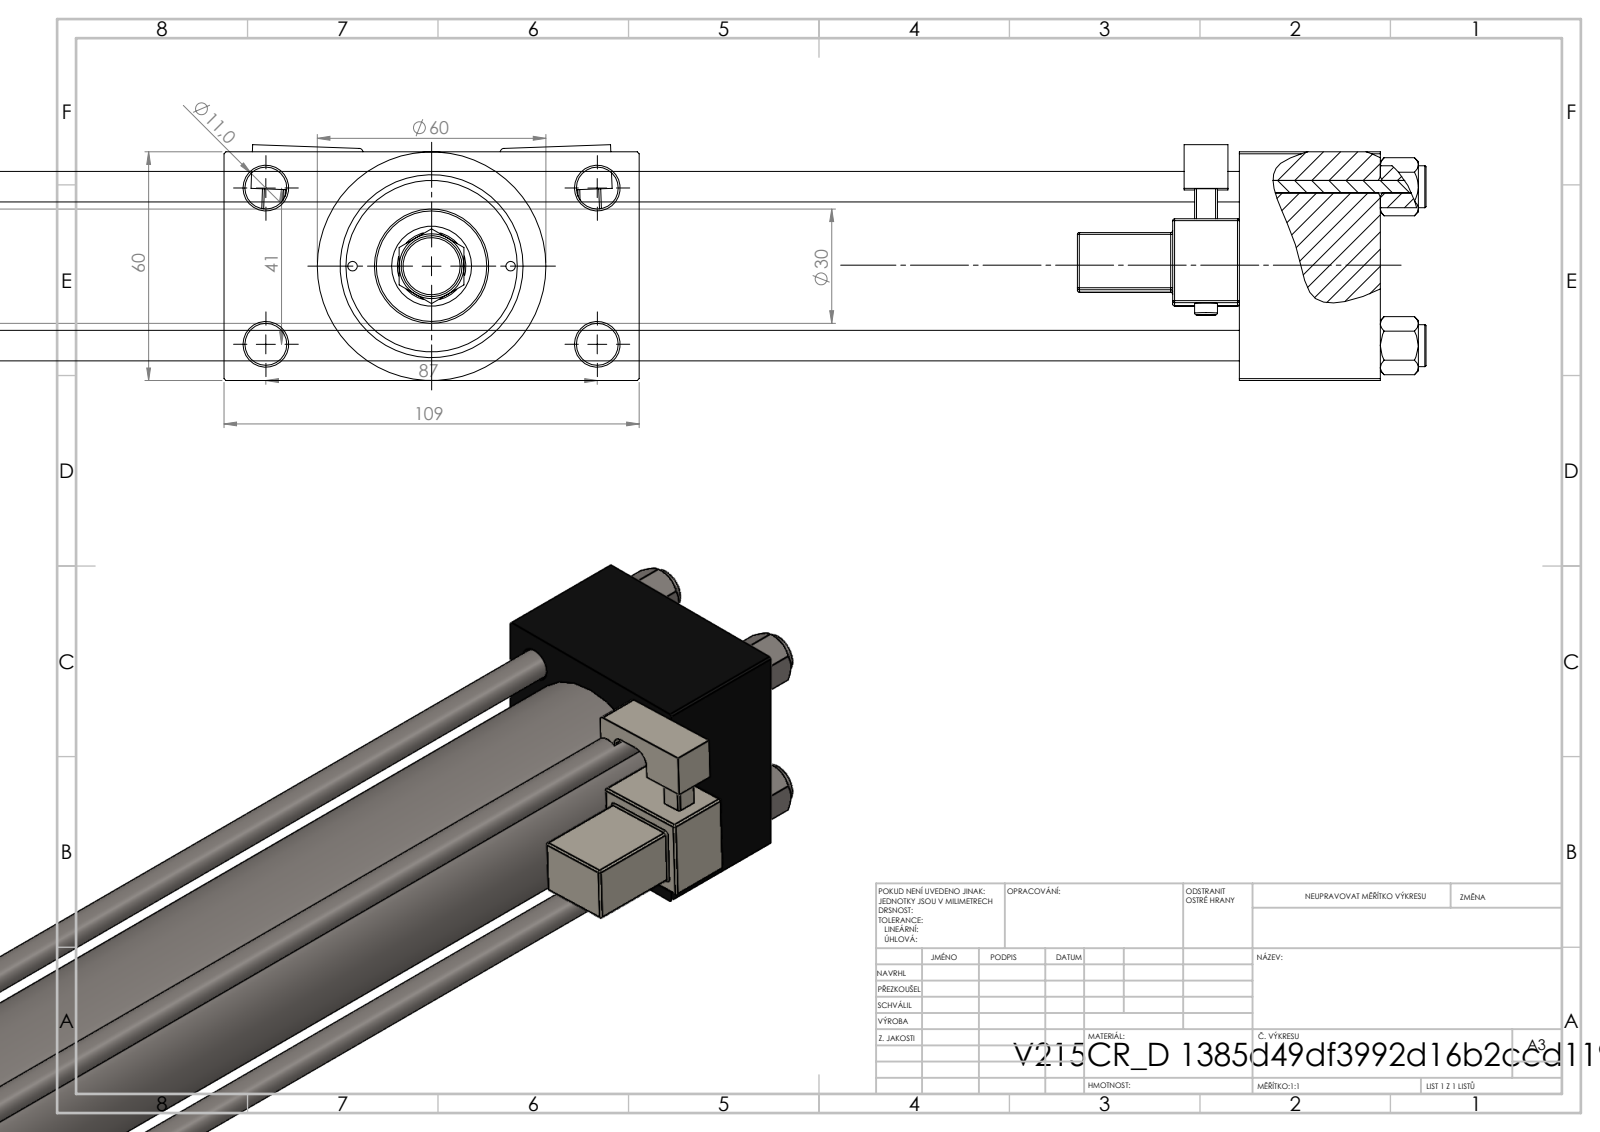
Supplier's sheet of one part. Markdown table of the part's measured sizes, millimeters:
| quantity | value |
| --- | --- |
| part name | V215_VC_A; V215CR_MSU; MFA; V215CR_D_TYCINKA (+3 more) |
| STEP written by | SolidWorks 2019 (CONFIG_CONTROL_DESIGN) |
| units | millimeters |
| bodies | 14 solids, 1318 faces (574 planar, 156 cylindrical, 588 other) |
| overall size | 543 × 109 × 61.9 |
| volume | 842 635 mm³ |
| surface area | 277 650 mm² |
| round holes (diameter × count) | 8 × 4, 11 × 4, 2.5 × 2, 7 × 2, 16.66 × 2, 24 × 2, 8.5 × 1, 18 × 1, 21 × 1, 31 × 1, 40 × 1, 45 × 1 |
| round bosses / shafts (diameter × count) | 11 × 4, 6 × 2, 60 × 1, 46 × 1, 30 × 1, 16 × 1, 10 × 1 |
| partial cylindrical surfaces (radius × count) | 0.5 × 48, 1 × 2, 2.5 × 2, 4 × 2, 8.5 × 1 |
| main face-to-face distances | 60, 388, 24.5, 84.5, 37, 425, 468, 431, 43, 109 |
| hole center spacings | 20.85, 22.65, 29.49, 30.62, 41.7, 46.53, 47.15, 48.09 |
